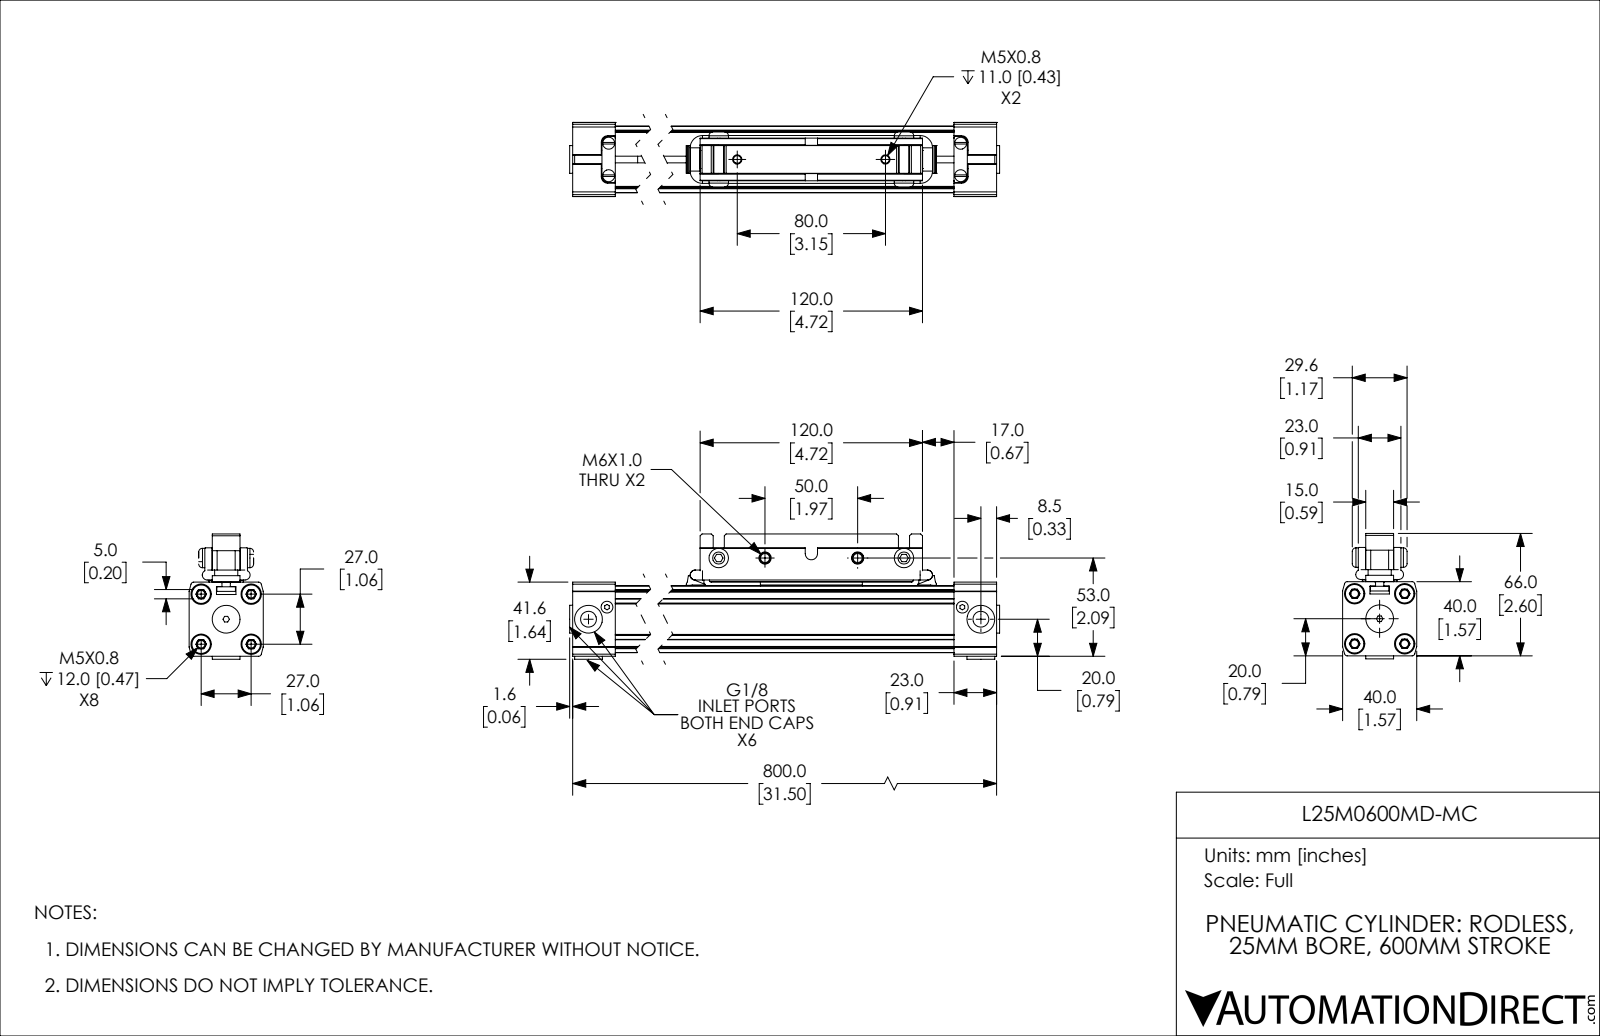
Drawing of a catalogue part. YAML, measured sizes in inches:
part_name: "L25M0600MD-MC; L25M0600MD-MC_BODY; L25M0600MD-MC_PISTON"
step_written_by: "SolidWorks 2019 (CONFIG_CONTROL_DESIGN)"
units: inches
bodies: {solids: 13, faces: 883, planar: 453, cylindrical: 322, other: 108}
overall_size: [31.625, 2.663, 1.575]
volume: 45.56
surface_area: 405.5
round_holes:
  - {diameter: 0.163, count: 6}
  - {diameter: 0.337, count: 5}
  - {diameter: 0.591, count: 5}
  - {diameter: 0.256, count: 4}
  - {diameter: 0.26, count: 4}
  - {diameter: 0.433, count: 4}
  - {diameter: 0.194, count: 2}
  - {diameter: 0.194, count: 2}
  - {diameter: 0.252, count: 2}
  - {diameter: 0.988, count: 1}
round_bosses_or_shafts:
  - {diameter: 0.394, count: 4}
  - {diameter: 0.383, count: 3}
  - {diameter: 0.323, count: 3}
  - {diameter: 0.413, count: 2}
  - {diameter: 0.21, count: 2}
  - {diameter: 0.21, count: 2}
  - {diameter: 0.984, count: 1}
partial_cylinders:
  - {radius: 0.012, count: 28}
  - {radius: 0.02, count: 14}
  - {radius: 0.039, count: 14}
  - {radius: 0.01, count: 12}
  - {radius: 0.138, count: 8}
  - {radius: 0.025, count: 6}
  - {radius: 0.059, count: 6}
  - {radius: 0.094, count: 6}
face_to_face_distances: [1.413, 1.417, 0.635, 0.777, 0.429, 0.079, 0.335, 0.906, 1.496, 0.224]
hole_center_spacings: [0.55, 0.752, 1.063, 30.4, 0.47, 0.689, 0.698, 0.809]
